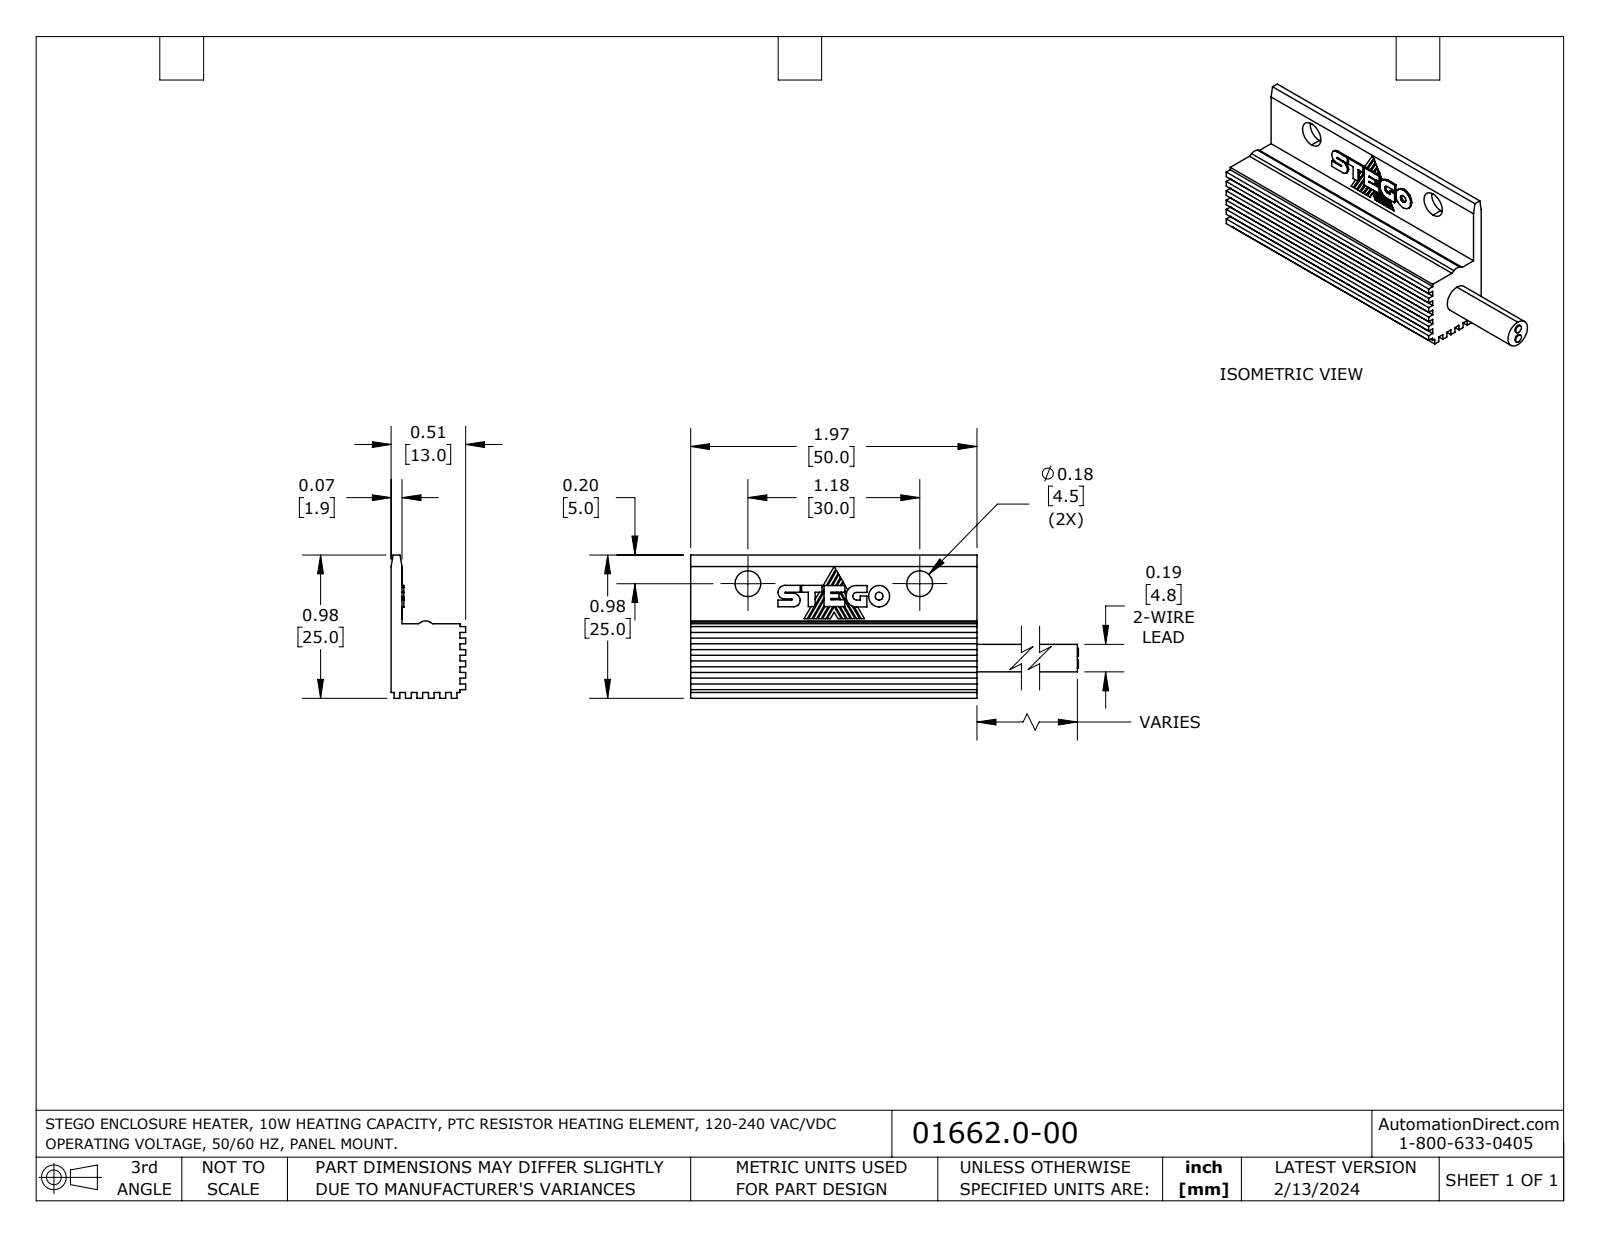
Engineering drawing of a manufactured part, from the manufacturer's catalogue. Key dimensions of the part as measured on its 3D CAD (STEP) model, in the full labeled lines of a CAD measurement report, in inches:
Part name (STEP PRODUCT): RC_016_50mm_EPLAN_08_2022
STEP written by: SolidWorks 2022 (AUTOMOTIVE_DESIGN)
Units: inches
Bodies: 1 solid, 249 faces (190 planar, 13 cylindrical, 46 other)
Overall size (bounding box): 2.567 × 0.984 × 0.512
Volume: 0.56 in³ · Surface area: 8.348 in²
Round holes (diameter × count): ⌀0.177 ×2
Round bosses / shafts (diameter × count): ⌀0.055 ×2, ⌀0.189 ×1
Partial cylindrical surfaces — rounded edges, fillets, slot ends (radius × count): R0.059 ×1, R0.072 ×1, R0.08 ×1
Main face-to-face distances: 0.039, 0.079, 0.118, 0.157, 0.197, 0.472, 0.512, 0.236, 0.276, 0.315
Hole centre spacings: 1.181
